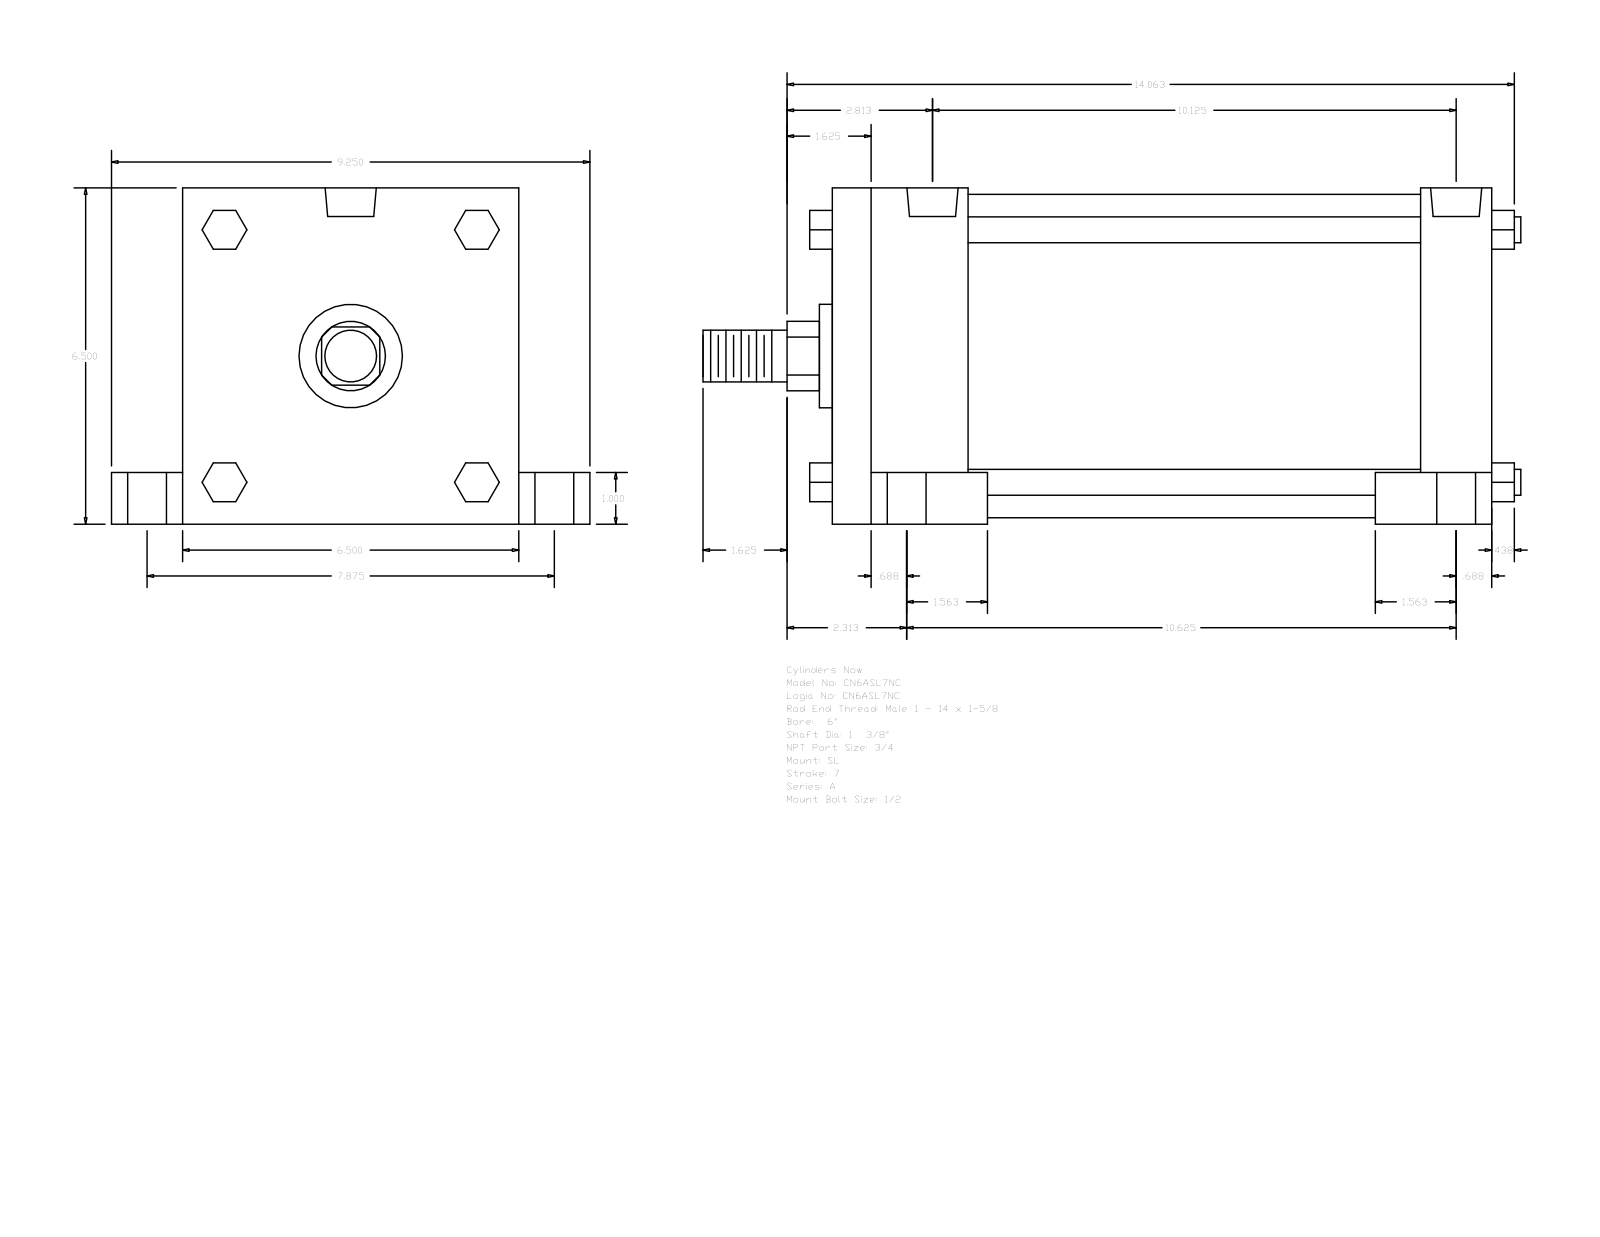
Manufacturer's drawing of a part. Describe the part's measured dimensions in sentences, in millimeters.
The part is named "A_SL__0600_1.375". Its 3-D file was written by "GSSL Pune (CONFIG_CONTROL_DESIGN)". It is 0 solids with 150 faces: 114 planar, 36 cylindrical and 0 other. Overall it measures 401.64 by 234.95 by 165.1 millimeters. Round holes: 4 of diameter 15.08, 4 of diameter 19.05, 4 of diameter 25.4, 2 of diameter 25.12. Round bosses or shafts: 4 of diameter 12.7, 1 of diameter 158.75, 1 of diameter 50.8, 1 of diameter 34.92, 1 of diameter 25.4. Partial cylindrical surfaces (rounded edges, fillets, slot ends): 1 of radius 17.06. The main face-to-face distances are 165.1, 323.84, 34.92, 66.67, 257.17, 288.92, 222.25, 25.4, 139.7, 200.02. The hole center spacings are 5.56, 100.01, 100.16, 100.81, 101.66, 200.02, 246.05, 251.61.
